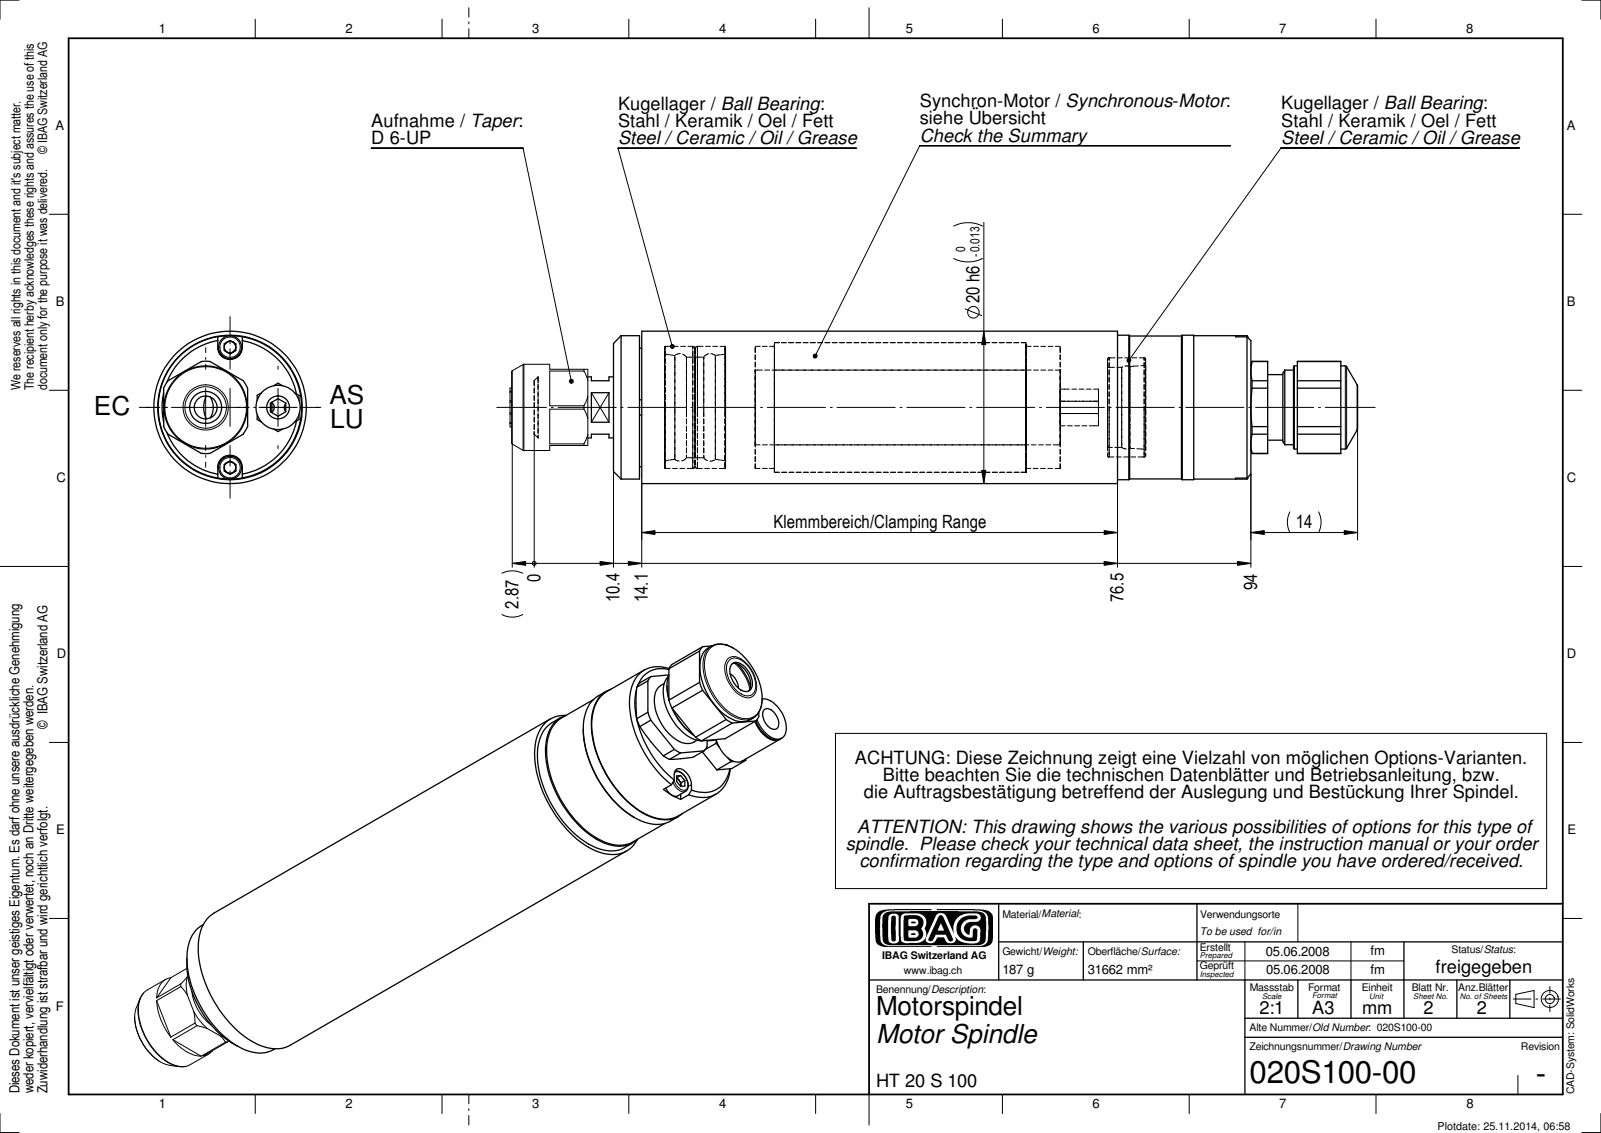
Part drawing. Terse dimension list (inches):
name: 020S100-00
written by: SolidWorks 2010 (CONFIG_CONTROL_DESIGN)
unit: in
bodies: 0 solids, 239 faces (110 planar, 85 cylindrical, 44 other)
size: 4.377 × 0.787 × 0.787
holes: 4× ⌀0.063, 2× ⌀0.118, 1× ⌀0.02, 1× ⌀0.165, 1× ⌀0.36
bosses: 2× ⌀0.118, 1× ⌀0.787, 1× ⌀0.746, 1× ⌀0.74, 1× ⌀0.738, 1× ⌀0.445, 1× ⌀0.429, 1× ⌀0.385
rounds: 2× R0.063, 1× R0.03, 1× R0.238
face distances: 0.394, 3.291, 0.295, 0.433, 2.996, 0.689, 0.146, 2.85, 3.146, 0.087
hole spacings: 0.207, 0.292, 0.242, 0.323, 0.413, 0.041, 0.081, 0.126
